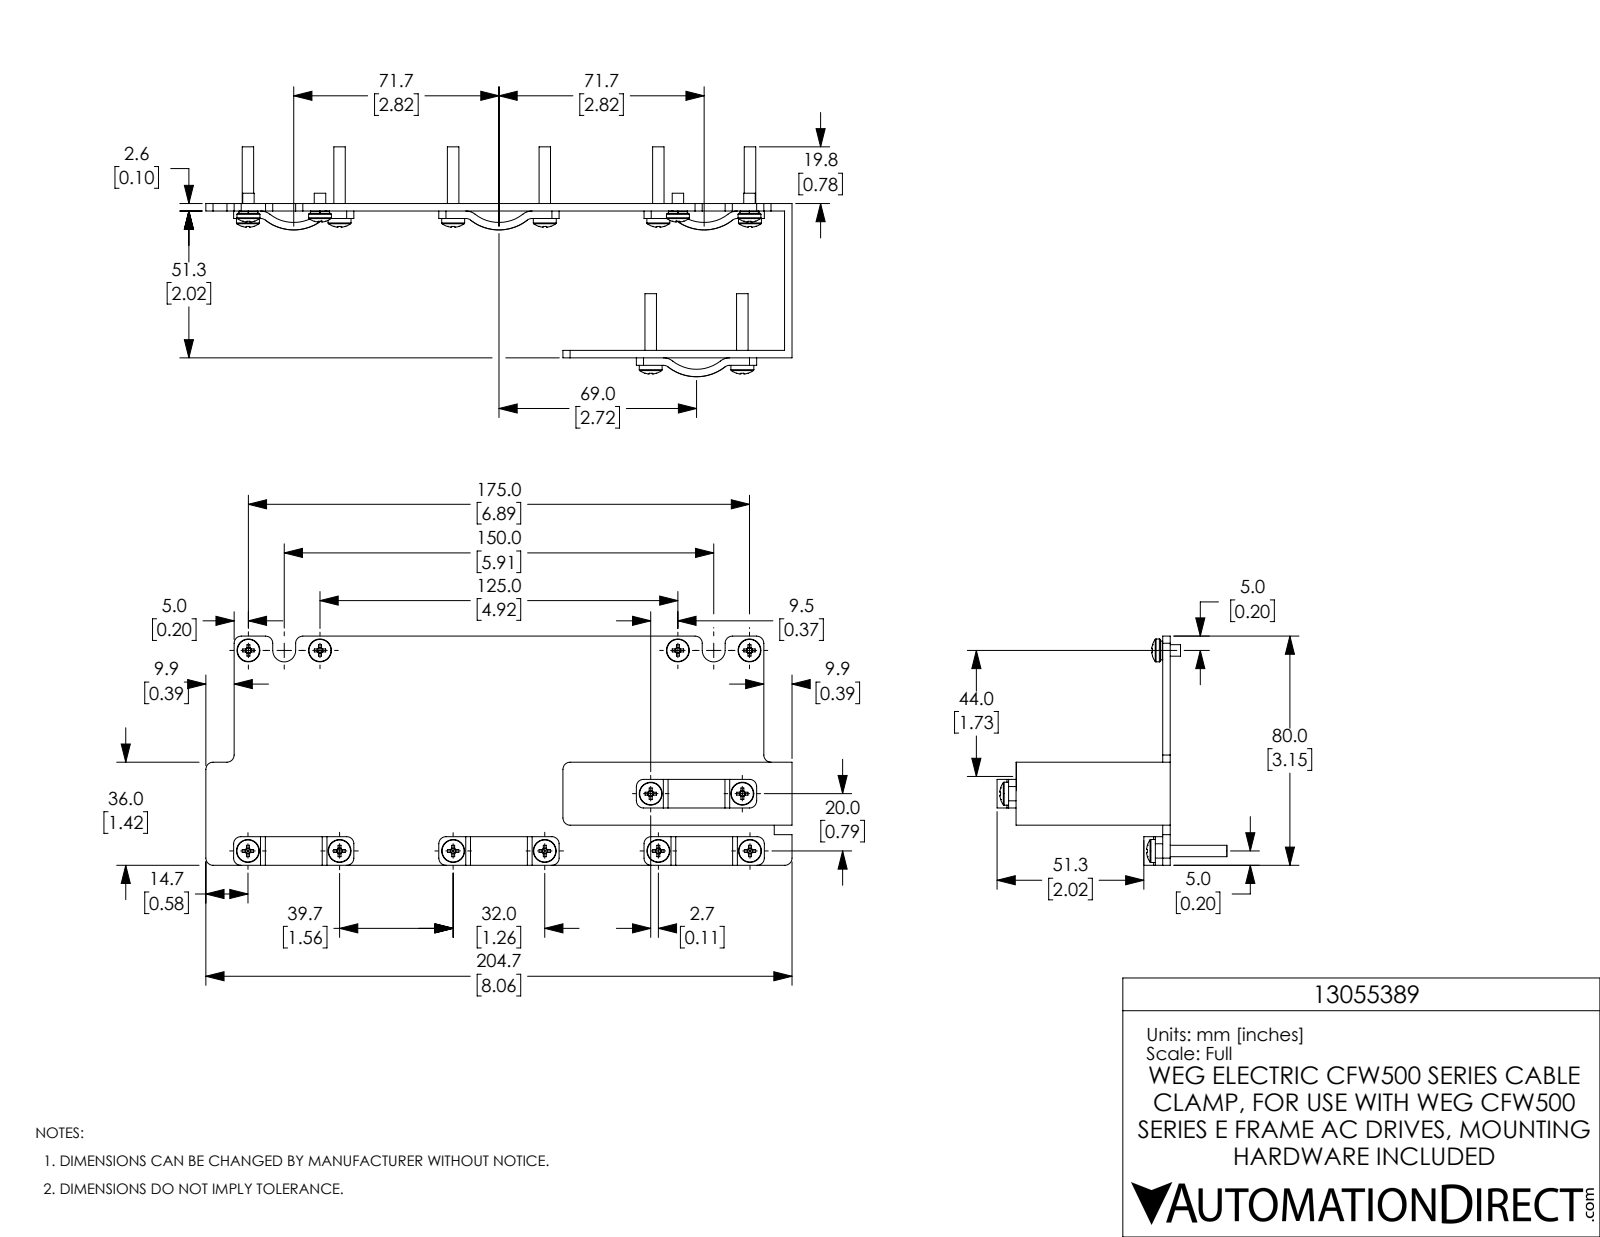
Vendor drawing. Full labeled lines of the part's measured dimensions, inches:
Part name (STEP PRODUCT): 13055389_CONJ BLINDAGEM CABOS CFW500_KPCSE NC
STEP written by: SolidWorks 2017 (AUTOMOTIVE_DESIGN)
Units: inches
Bodies: 17 solids, 639 faces (292 planar, 175 cylindrical, 172 other)
Overall size (bounding box): 8.059 × 3.159 × 3.15
Volume: 3.378 in³ · Surface area: 75.04 in²
Round holes (diameter × count): ⌀0.13 ×10, ⌀0.177 ×10, ⌀0.148 ×4
Round bosses / shafts (diameter × count): ⌀0.315 ×12, ⌀0.157 ×12, ⌀0.26 ×4, ⌀0.126 ×4
Partial cylindrical surfaces — rounded edges, fillets, slot ends (radius × count): R0.098 ×29, R0.106 ×8, R0.209 ×8, R0.531 ×4, R0.634 ×4, R0.157 ×2
Main face-to-face distances: 0.102, 2.018, 1.915, 2.12, 0.205, 1.813, 0.394, 3.15, 1.417, 1.732
Hole centre spacings: 1.26, 2.822, 0.794, 0.984, 1.562, 2.756, 2.769, 2.828
